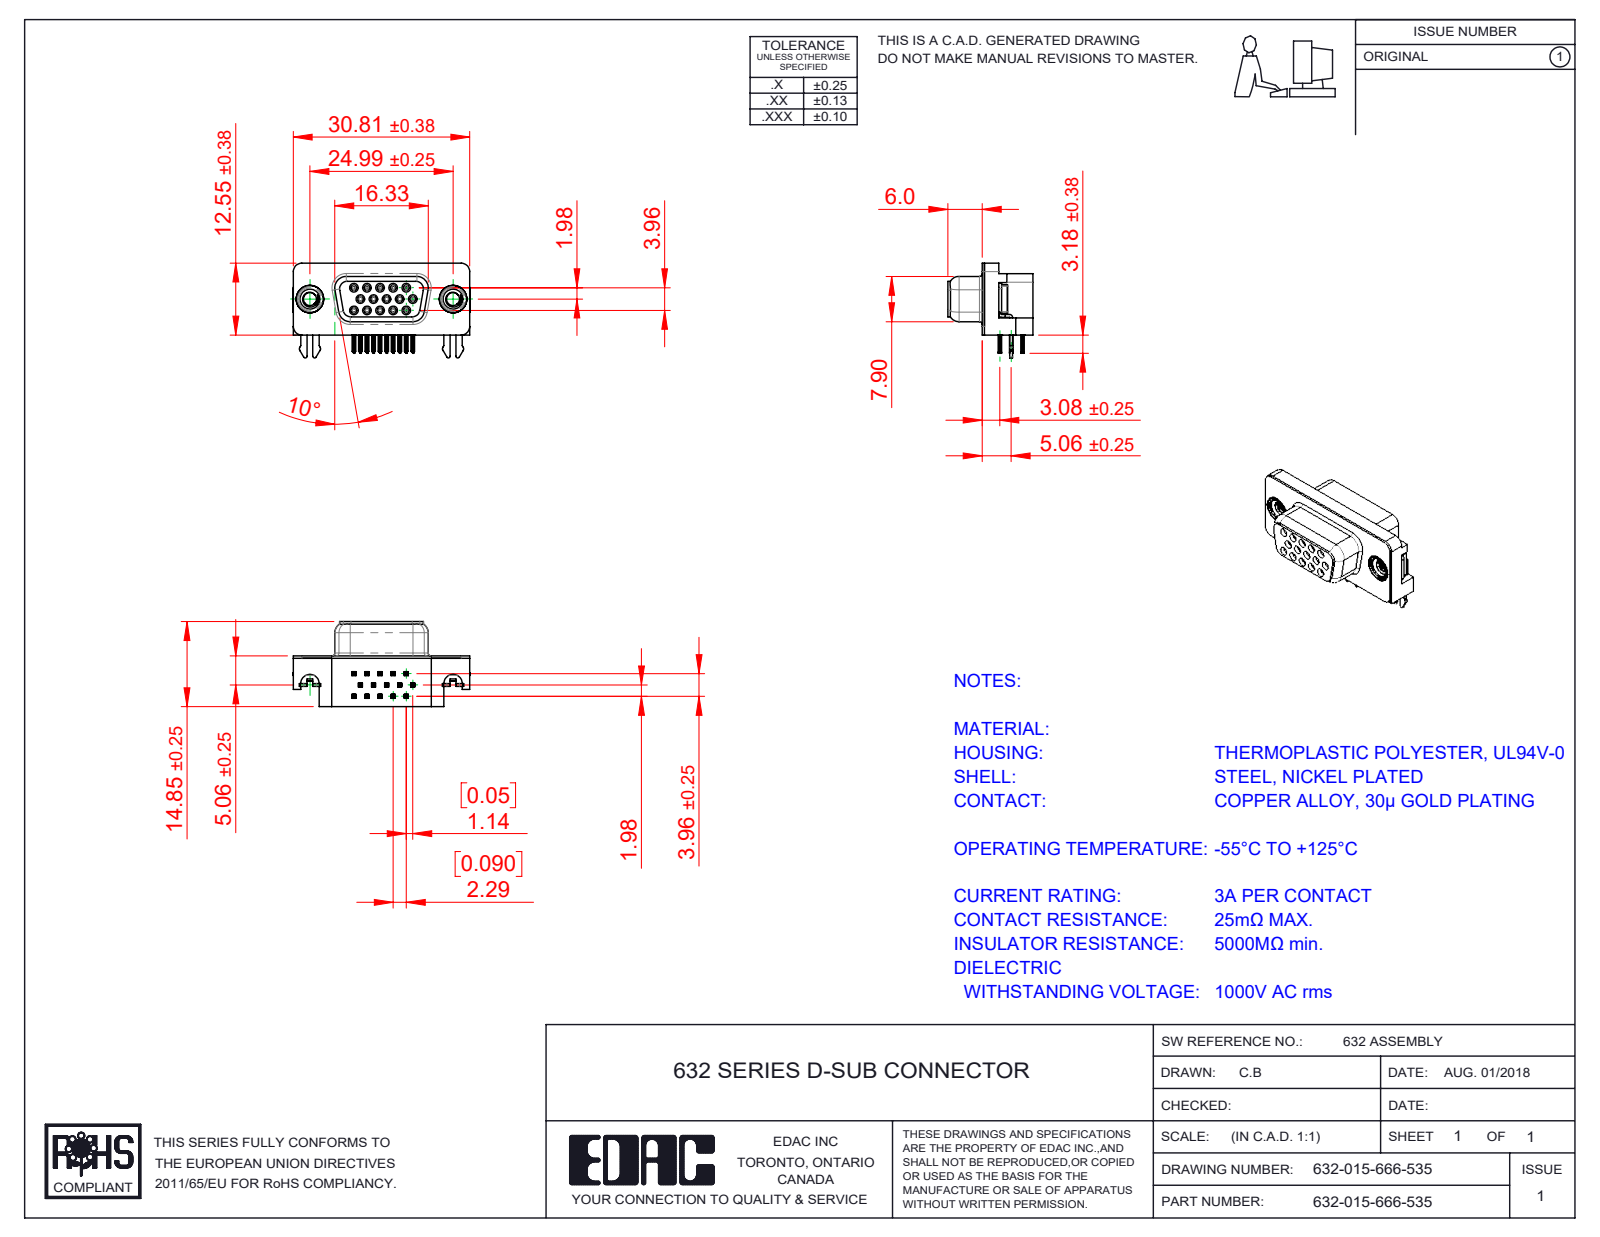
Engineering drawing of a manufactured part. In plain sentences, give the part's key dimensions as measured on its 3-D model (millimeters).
The part is named "632 4-40 Threaded Rivet; 632 M3 Threaded Rivet; 632 2 Prong Board Lock; 632 Housing_15 Socket (+5 more)". Its 3-D file was written by "SolidWorks 2016 (CONFIG_CONTROL_DESIGN)". It is 23 solids with 2426 faces: 1006 planar, 654 cylindrical and 766 other. Overall it measures 30.89 by 16.55 by 14.85 millimeters. Its volume is 2 996 cubic millimeters and its surface area 5 342 square millimeters. Round holes: 15 of diameter 0.8, 15 of diameter 0.9, 2 of diameter 2.26, 2 of diameter 2.5, 2 of diameter 4, 2 of diameter 4.8, 2 of diameter 5. Round bosses or shafts: 15 of diameter 1.2, 2 of diameter 4.9, 2 of diameter 4.75, 2 of diameter 3.9. Partial cylindrical surfaces (rounded edges, fillets, slot ends): 120 of radius 0.1, 60 of radius 0.15, 30 of radius 0.35, 15 of radius 0.34, 11 of radius 1, 10 of radius 0.28, 10 of radius 0.5, 8 of radius 0.25. The main face-to-face distances are 0.4, 8.45, 8.85, 1.98, 2.9, 5.95, 2.5, 6.4, 6.7, 7.05. The hole center spacings are 2.28, 2.29, 3.96, 4.57, 6.05, 3.97, 4.58, 6.86.
